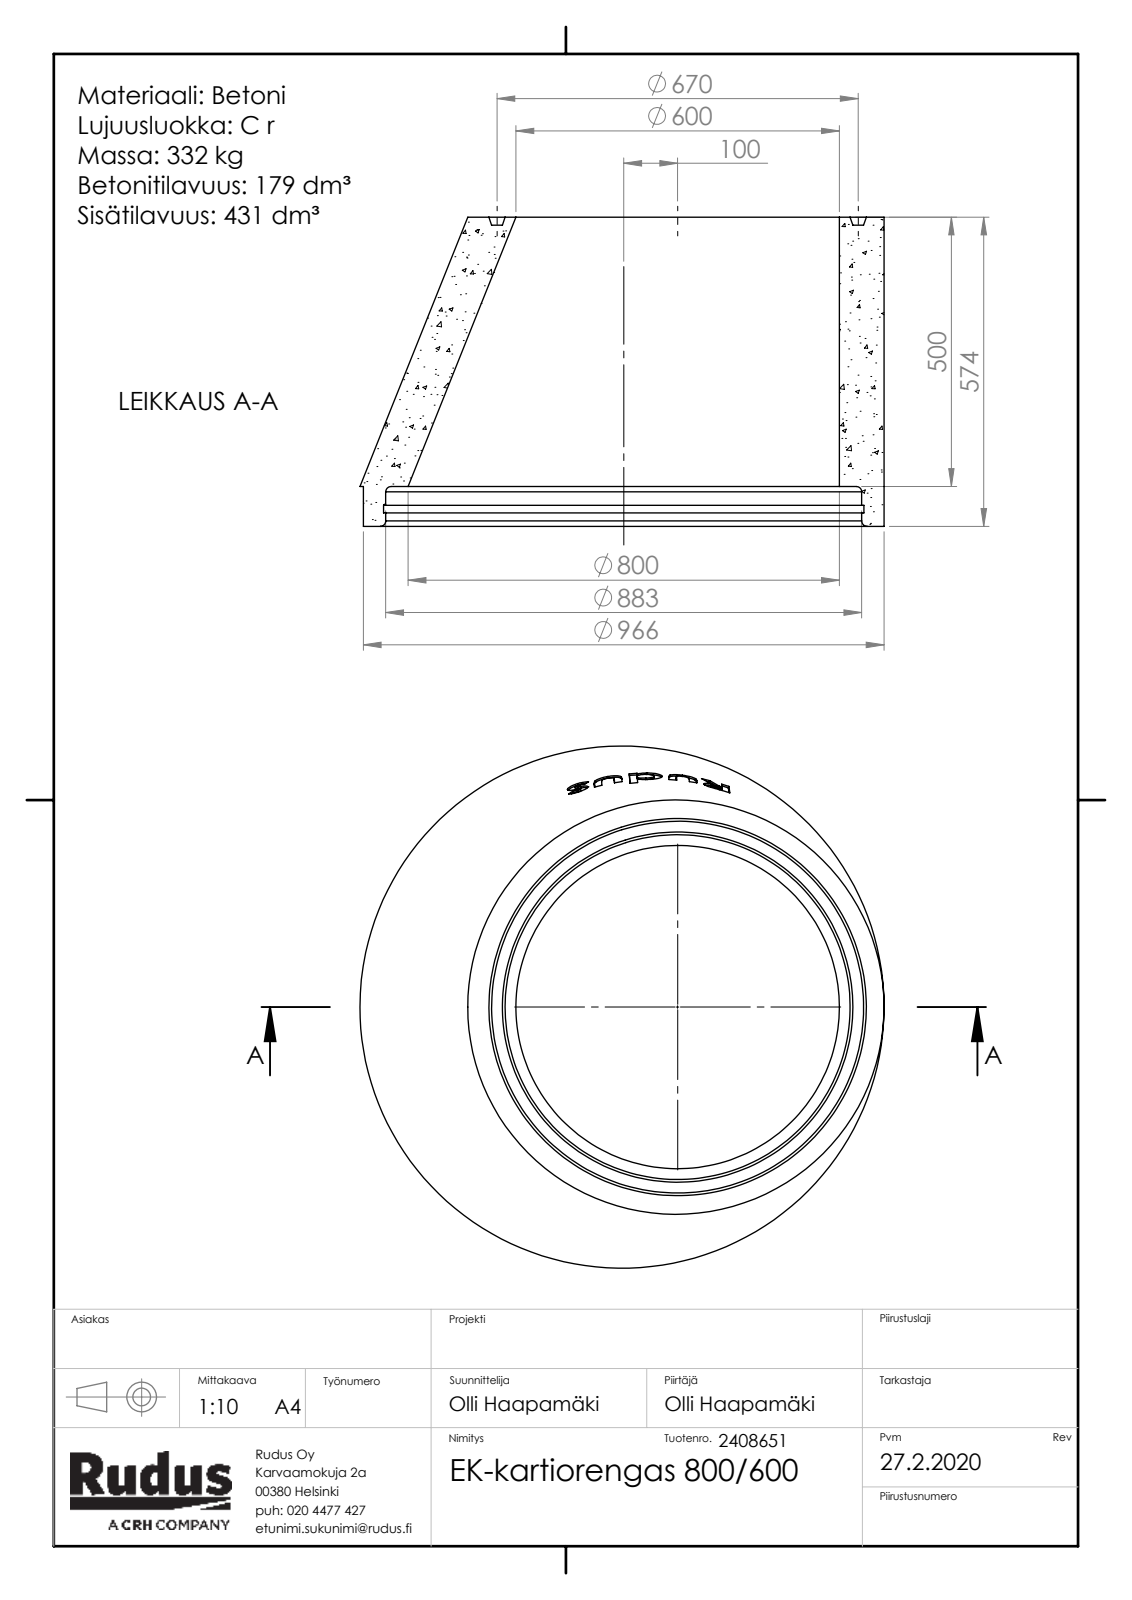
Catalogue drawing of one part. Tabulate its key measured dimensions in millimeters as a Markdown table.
| quantity | value |
| --- | --- |
| part name | EK-osa-kaivorunko_EK-kaivonrengas_lukitusuralla; Rudus 2408651 EK-kartiorengas 800-600 |
| STEP written by | SolidWorks 2019 (CONFIG_CONTROL_DESIGN) |
| units | millimeters |
| bodies | 1 solid, 105 faces (8 planar, 8 cylindrical, 89 other) |
| overall size | 972.39 × 969.29 × 574 |
| volume | 113 400 000 mm³ |
| surface area | 3 440 000 mm² |
| round holes (diameter × count) | 883 × 1, 891 × 1 |
| round bosses / shafts (diameter × count) | 966 × 1 |
| main face-to-face distances | 574, 74, 500, 559, 485, 15, 39, 35, 520, 535 |
